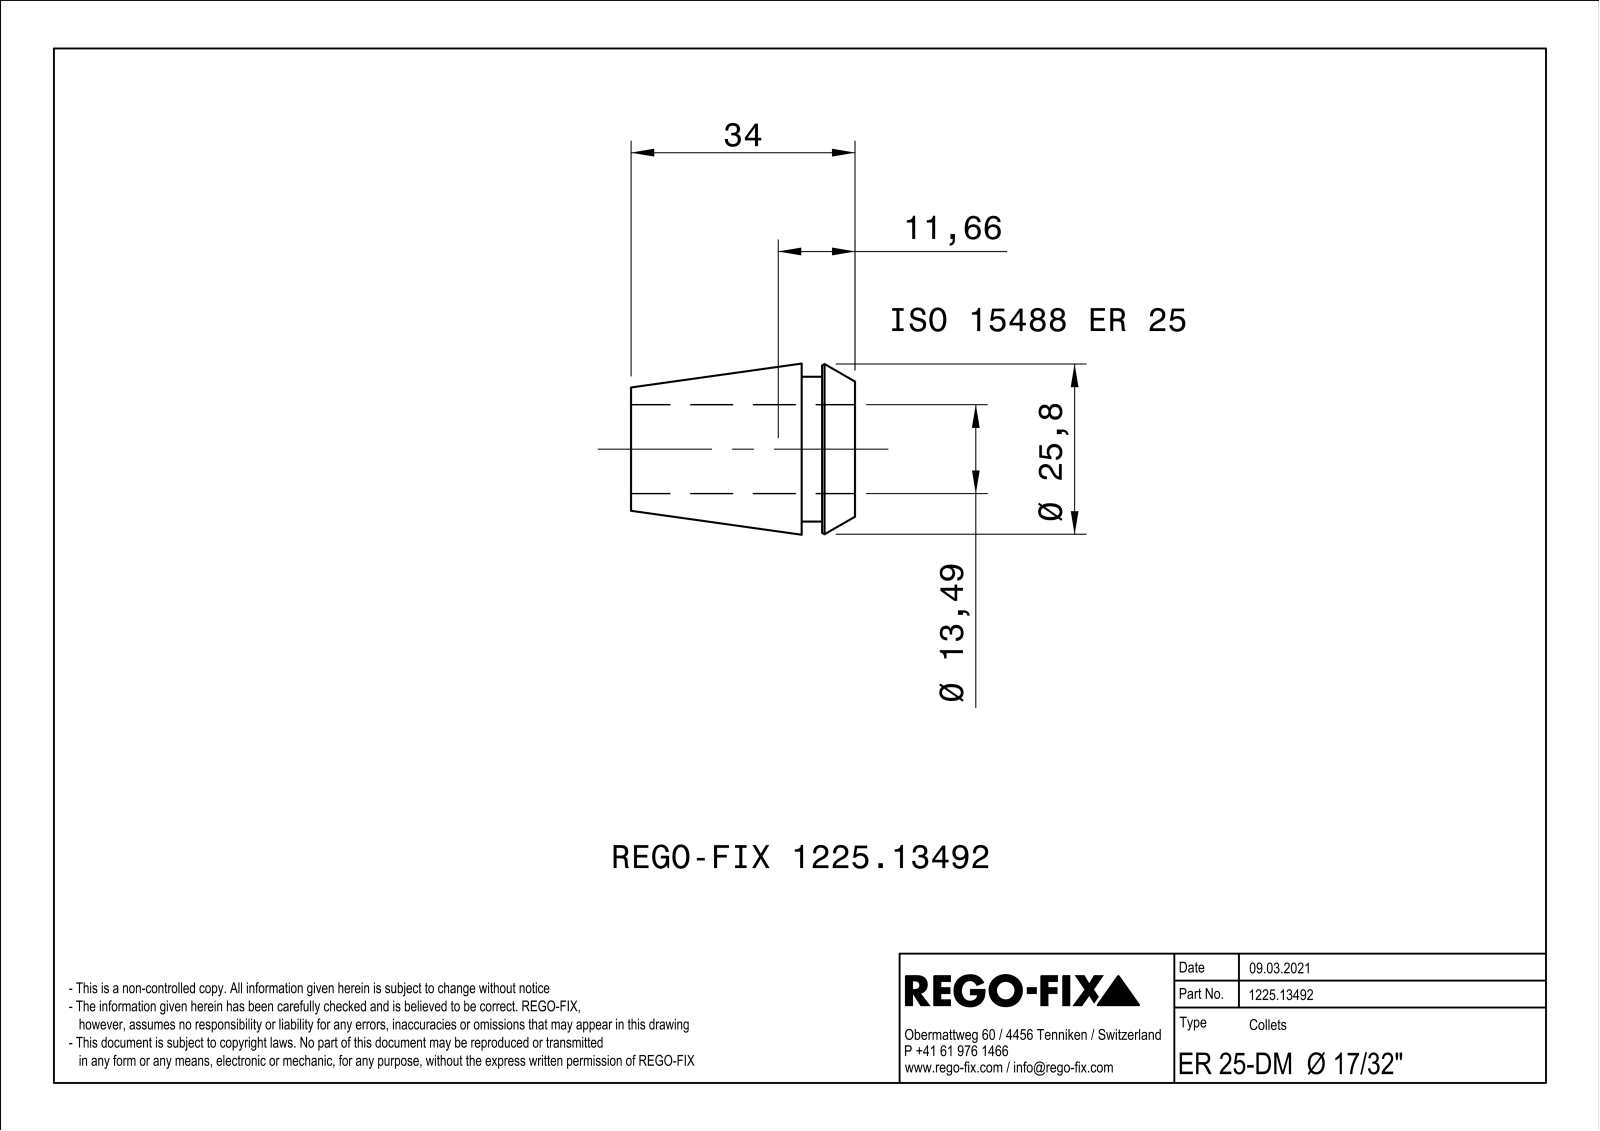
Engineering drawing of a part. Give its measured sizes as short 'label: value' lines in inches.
name: NOCUT
written by: SIEMENS PLM Software Solid Edge ST10 (AUTOMOTIVE_DESIGN)
unit: in
bodies: 1 solid, 154 faces (80 planar, 9 cylindrical, 65 other)
size: 1.339 × 1.023 × 1.023
volume: 0.45 in³; area: 11.27 in²
holes: 1× ⌀0.531
bosses: 1× ⌀0.866
face distances: 0.031, 0.319, 0.197, 1.142, 0.122, 1.339, 1.02, 0.591, 0.394, 0.272
